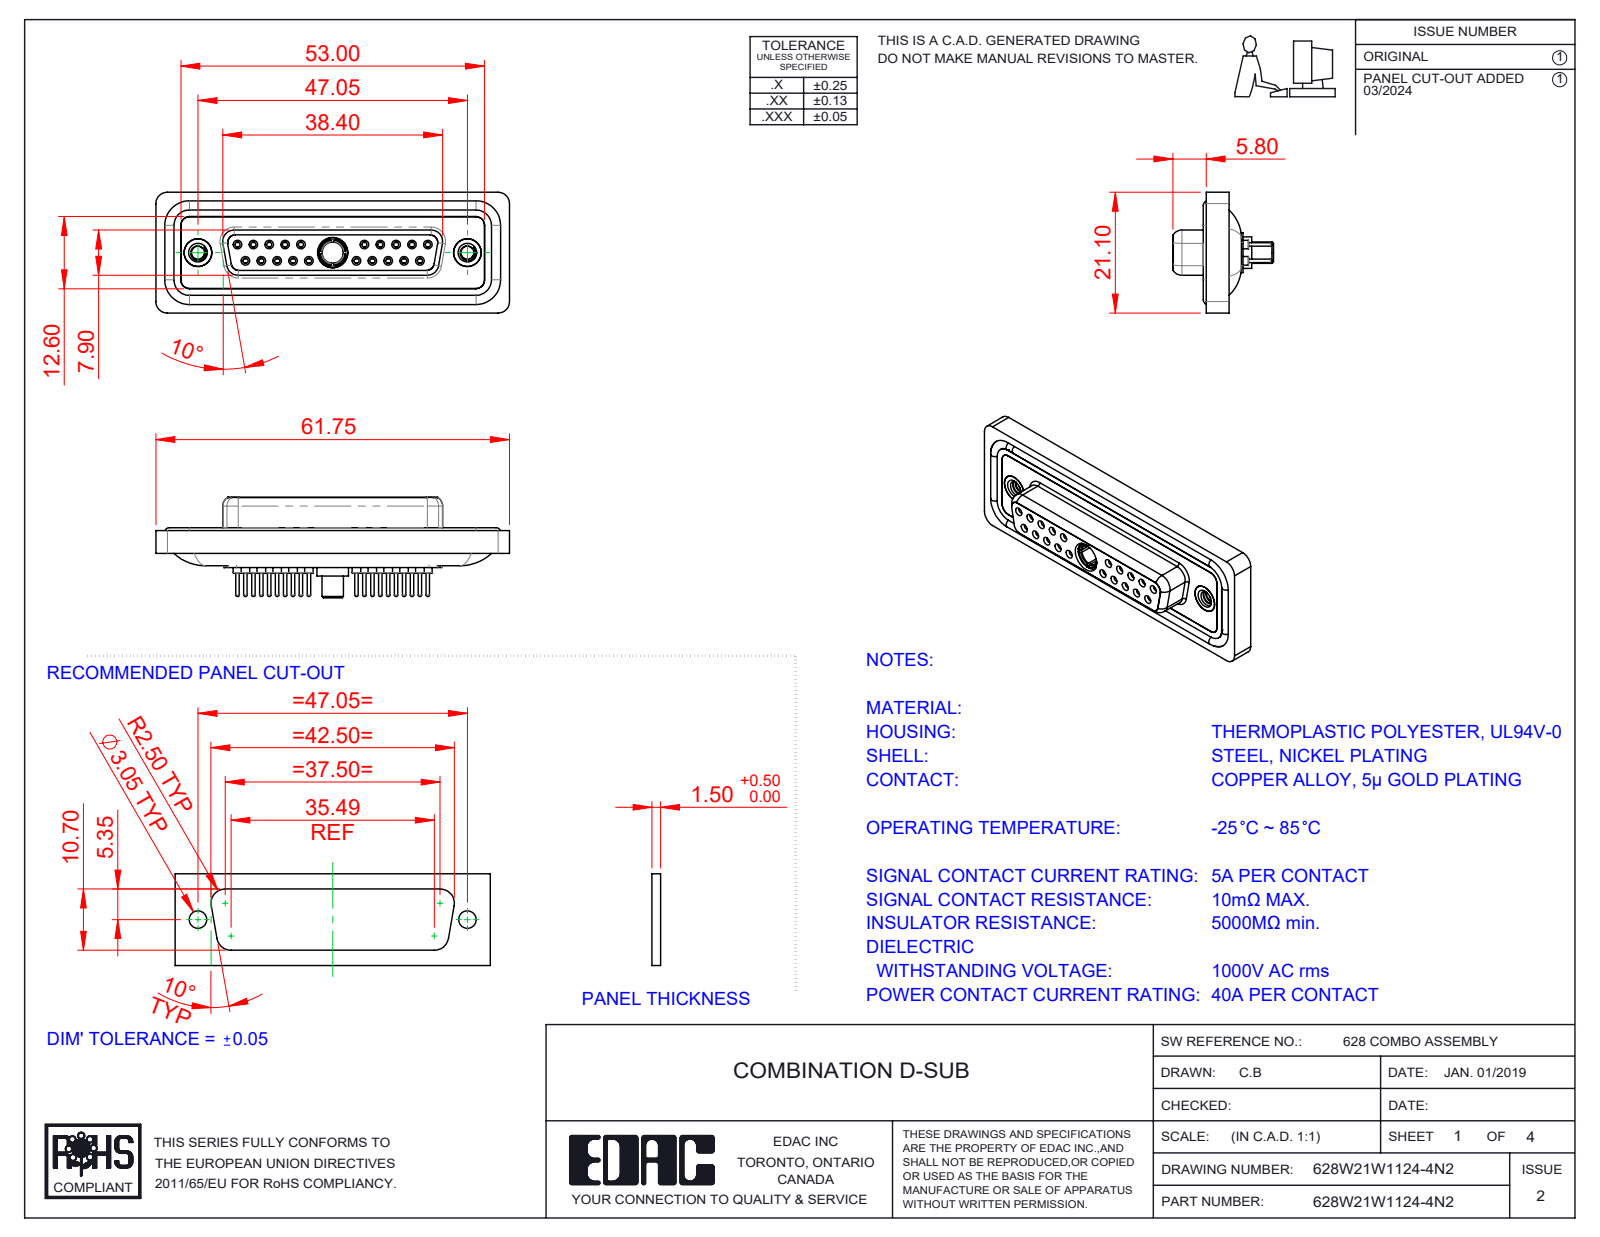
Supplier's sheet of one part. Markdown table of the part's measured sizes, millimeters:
| quantity | value |
| --- | --- |
| part name | 628Combo Contact Row 1_24; 628W21W1124-4N2; 628Combo Waterproof Housing_25 Contacts; Power Socket_40A S (+5 more) |
| STEP written by | SolidWorks 2023 (CONFIG_CONTROL_DESIGN) |
| units | millimeters |
| bodies | 29 solids, 1560 faces (434 planar, 591 cylindrical, 535 other) |
| overall size | 61.75 × 21.1 × 17.55 |
| volume | 8 393 mm³ |
| surface area | 14 013 mm² |
| round holes (diameter × count) | 0.9 × 20, 1.1 × 20, 1.5 × 20, 2 × 20, 1.6 × 10, 1.7 × 10, 4.85 × 3, 2.26 × 2, 4 × 2, 4.05 × 2, 5 × 2, 3.7 × 1 |
| round bosses / shafts (diameter × count) | 2.2 × 20, 0.6 × 20, 1.6 × 14, 4.95 × 2, 4.8 × 2, 5.5 × 1, 5.2 × 1, 4.96 × 1 |
| partial cylindrical surfaces (radius × count) | 1.5 × 22, 2 × 18, 1.35 × 8, 1.6 × 8, 0.25 × 4, 0.5 × 4, 0.6 × 4, 0.65 × 4 |
| main face-to-face distances | 0.4, 1.8, 7.45, 6.6, 5.65, 0.5, 1.6, 7.05, 2.9, 1.1 |
| hole center spacings | 3.16, 2.77, 5.54, 5.03, 8.31, 7.48, 16.62, 19.39 |
